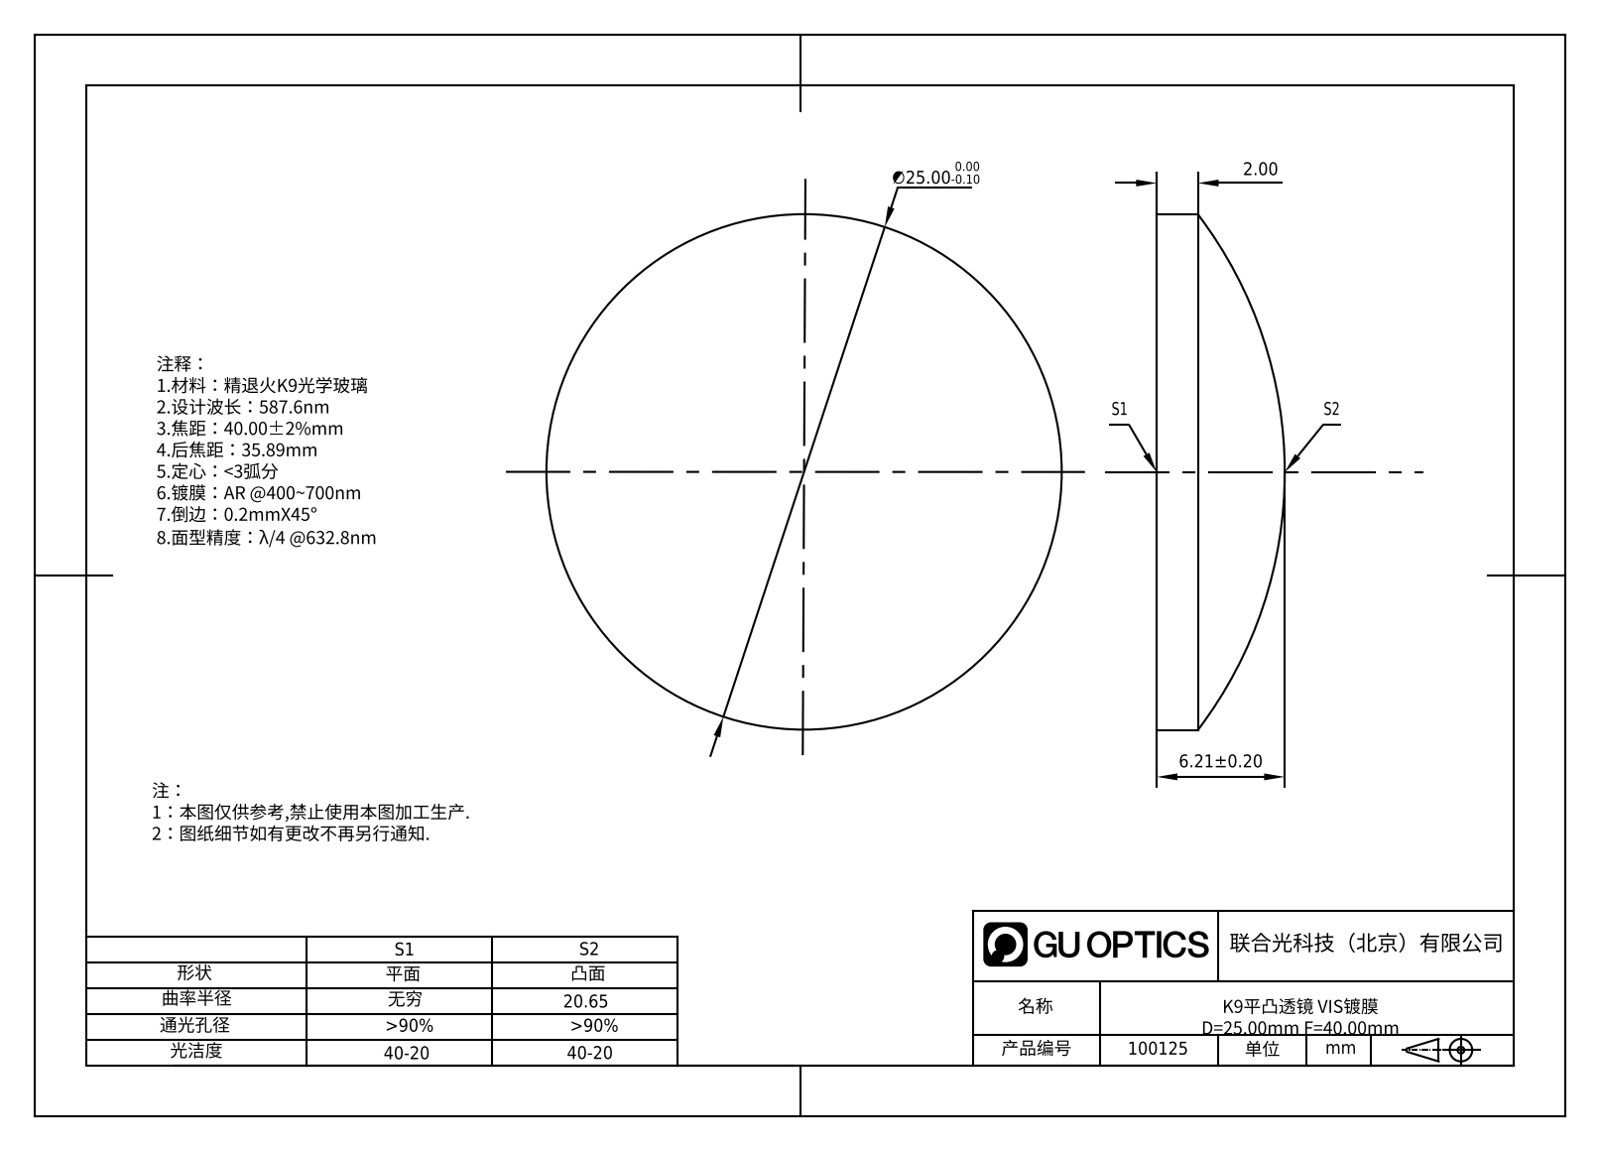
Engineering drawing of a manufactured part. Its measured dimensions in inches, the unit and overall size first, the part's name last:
Units: inches
Overall size (bounding box): 0.984 × 0.984 × 0.244
Round bosses / shafts (diameter × count): ⌀0.984 ×1
Volume: 0.125 in³ · Surface area: 1.852 in²
Bodies: 1 solid, 5 faces (1 planar, 2 cylindrical, 2 other)
Part name (STEP PRODUCT): 100125
STEP written by: SolidWorks 2016 (AUTOMOTIVE_DESIGN)
